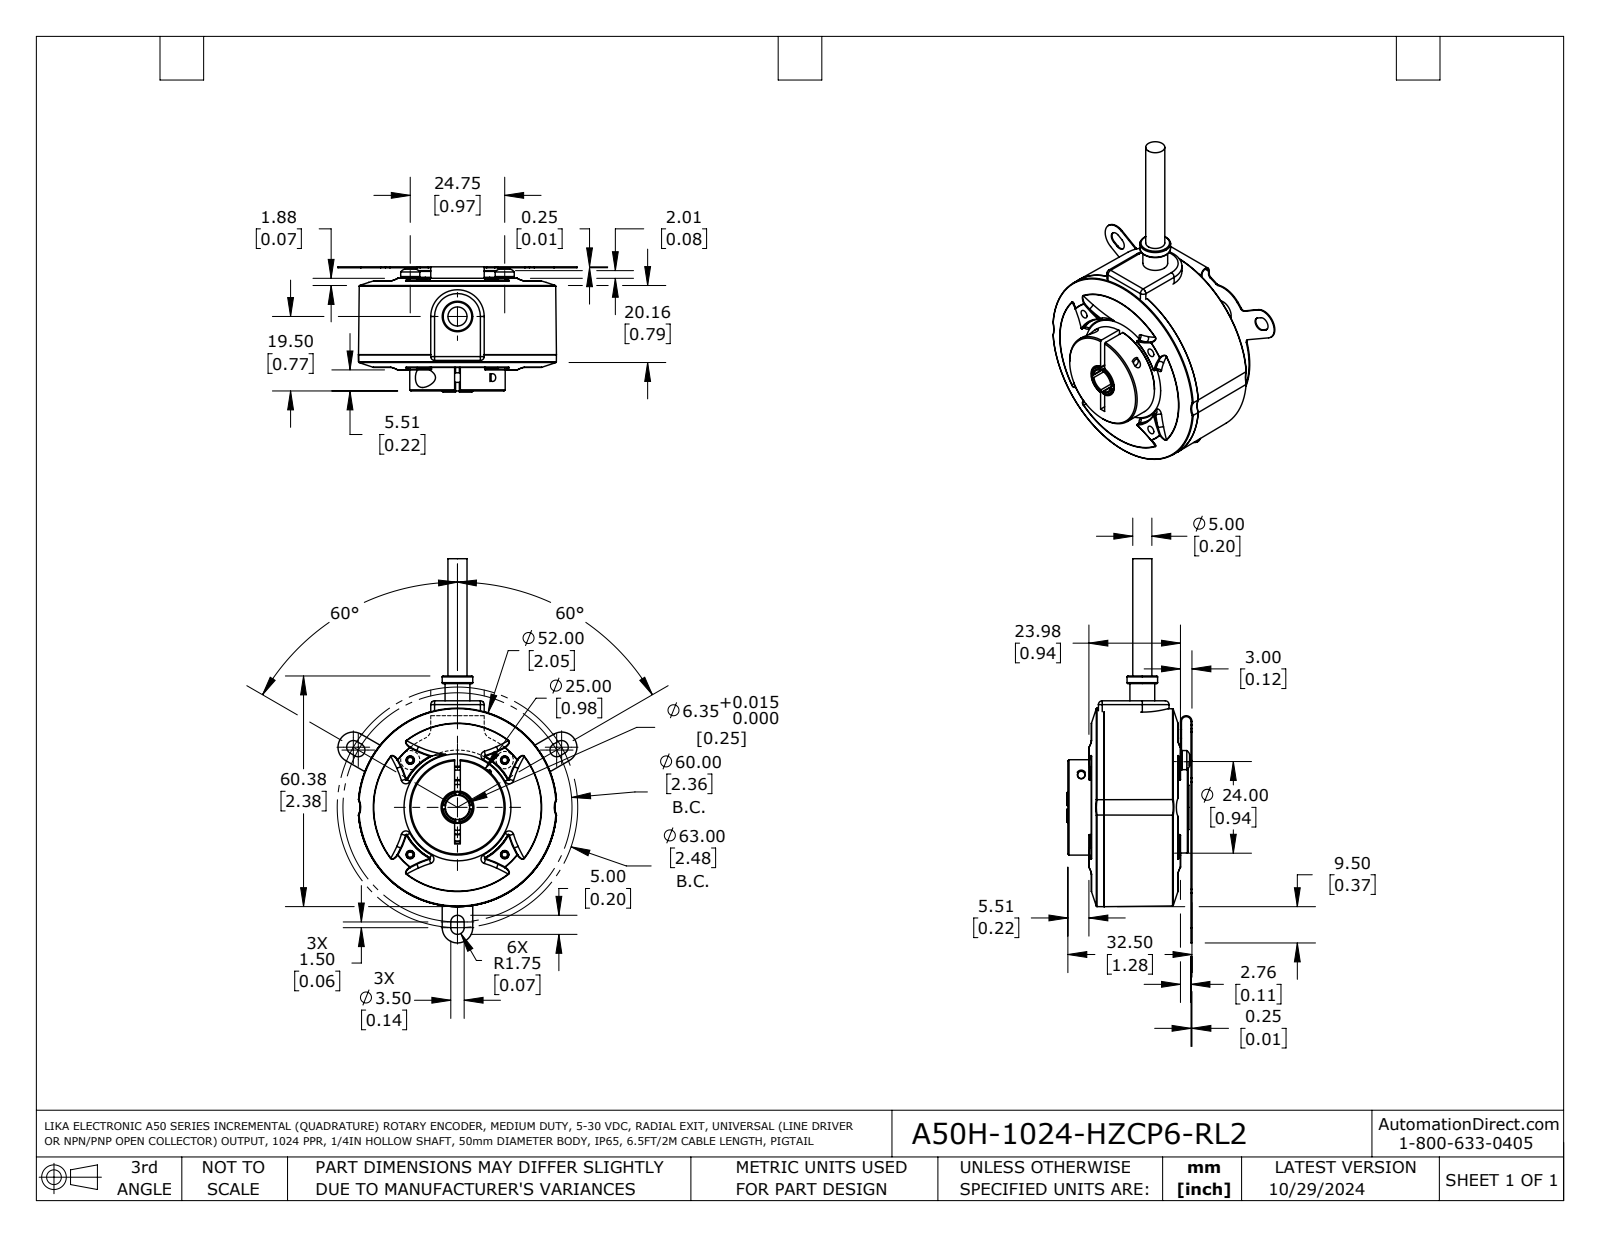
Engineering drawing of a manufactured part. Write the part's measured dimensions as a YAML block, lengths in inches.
part_name: "A50H-1024-HZCP6-RL2"
step_written_by: "SolidWorks 2021 (AUTOMOTIVE_DESIGN)"
units: inches
bodies: {solids: 14, faces: 954, planar: 160, cylindrical: 259, other: 535}
overall_size: [3.961, 2.464, 1.291]
volume: 1.39
surface_area: 43.48
round_holes:
  - {diameter: 0.11, count: 5}
  - {diameter: 0.217, count: 2}
  - {diameter: 0.236, count: 2}
  - {diameter: 0.081, count: 1}
  - {diameter: 0.205, count: 1}
  - {diameter: 0.25, count: 1}
  - {diameter: 0.315, count: 1}
  - {diameter: 0.579, count: 1}
  - {diameter: 0.728, count: 1}
  - {diameter: 1.024, count: 1}
round_bosses_or_shafts:
  - {diameter: 0.098, count: 5}
  - {diameter: 0.197, count: 4}
  - {diameter: 0.984, count: 1}
  - {diameter: 0.827, count: 1}
  - {diameter: 0.709, count: 1}
  - {diameter: 0.571, count: 1}
  - {diameter: 0.472, count: 1}
  - {diameter: 0.315, count: 1}
partial_cylinders:
  - {radius: 0.007, count: 24}
  - {radius: 0.015, count: 24}
  - {radius: 0.039, count: 18}
  - {radius: 0.004, count: 6}
  - {radius: 0.069, count: 6}
  - {radius: 0.984, count: 5}
  - {radius: 0.157, count: 3}
  - {radius: 0.02, count: 2}
face_to_face_distances: [0.118, 0.079, 0.787, 0.197, 0.669, 0.866, 0.896, 0.276, 0.748, 0.098]
hole_center_spacings: [0.583, 0.689, 0.807, 1.383, 0.974, 1.614]
